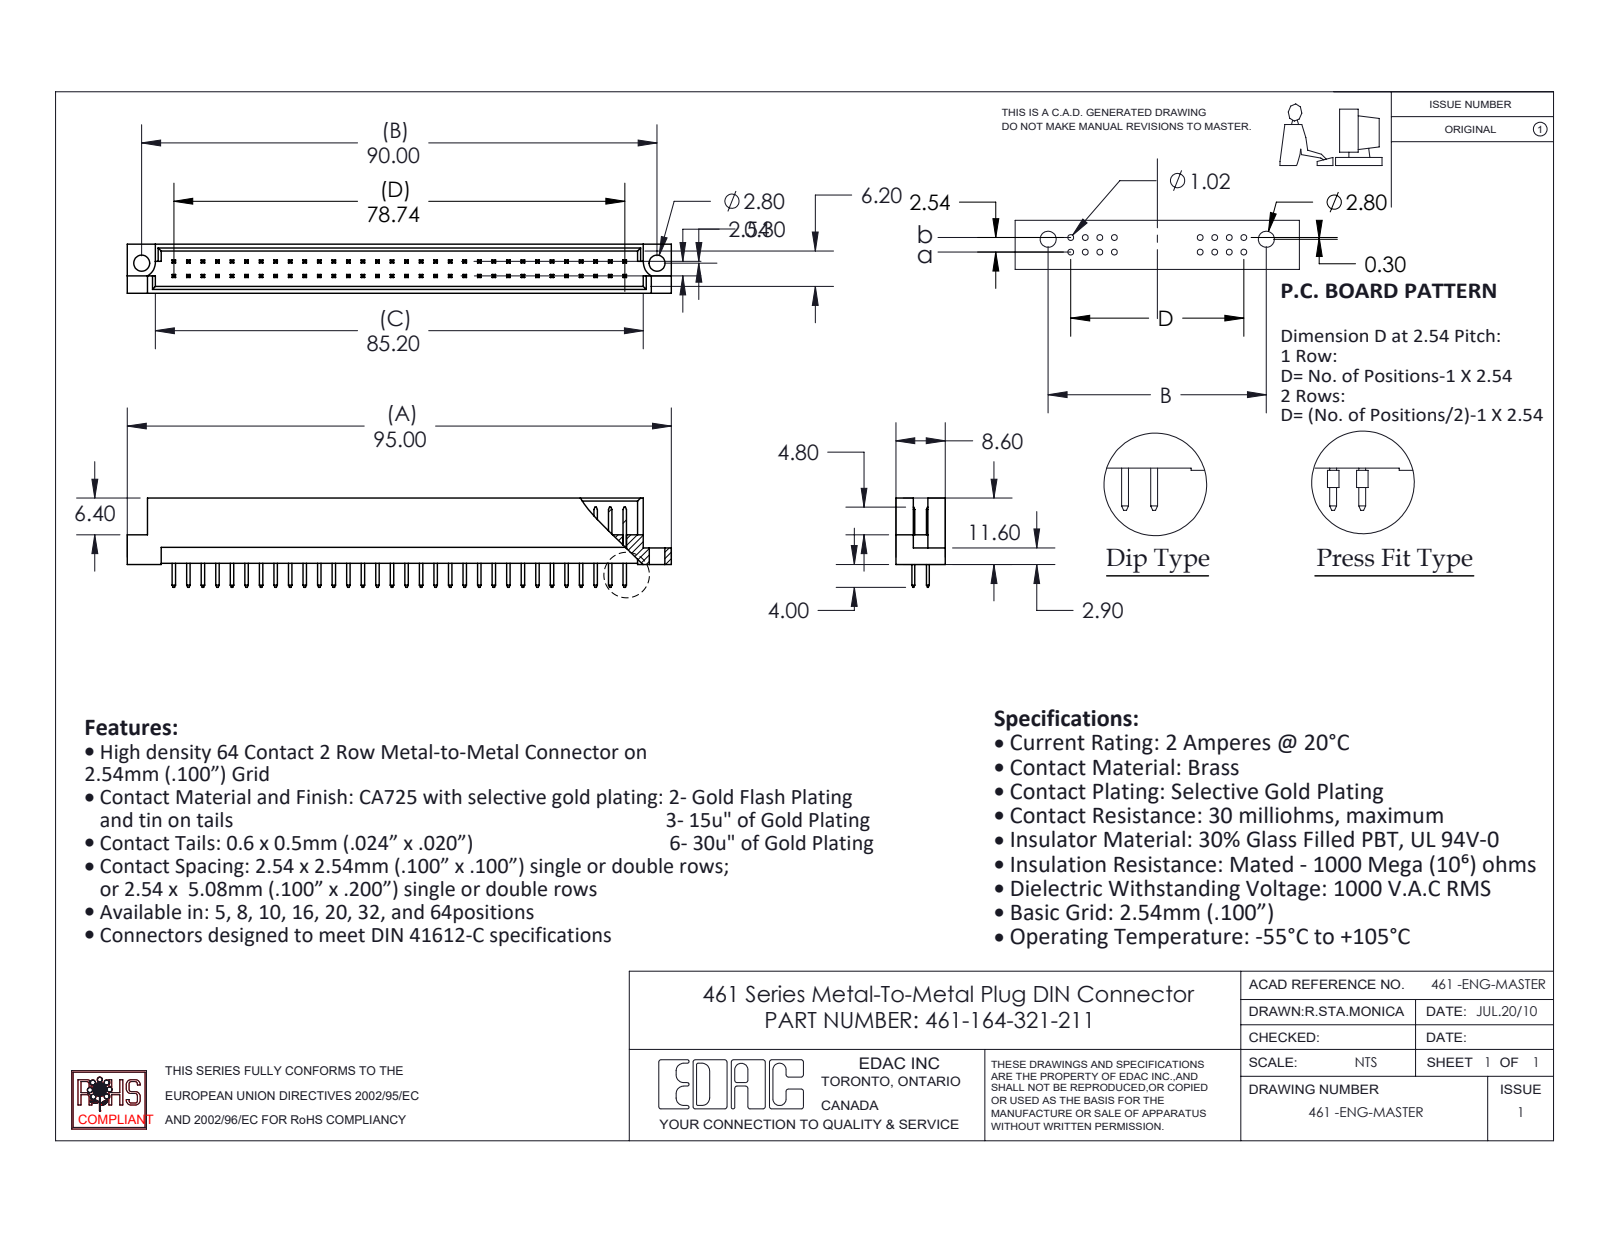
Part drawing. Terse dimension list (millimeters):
name: 461-164-321-211; 461-290_21; 461 Part_64
written by: SolidWorks 2020 (CONFIG_CONTROL_DESIGN)
unit: mm
bodies: 65 solids, 1201 faces (1194 planar, 7 cylindrical, 0 other)
size: 95 × 15.6 × 8.6
volume: 4 918 mm³; area: 7 618 mm²
holes: 2× ⌀2.8
rounds: 2× R2.8
face distances: 1.2, 7.4, 2.54, 8.6, 6.2, 3.28, 5.32, 2.08, 4.12, 2.78
hole spacings: 90
